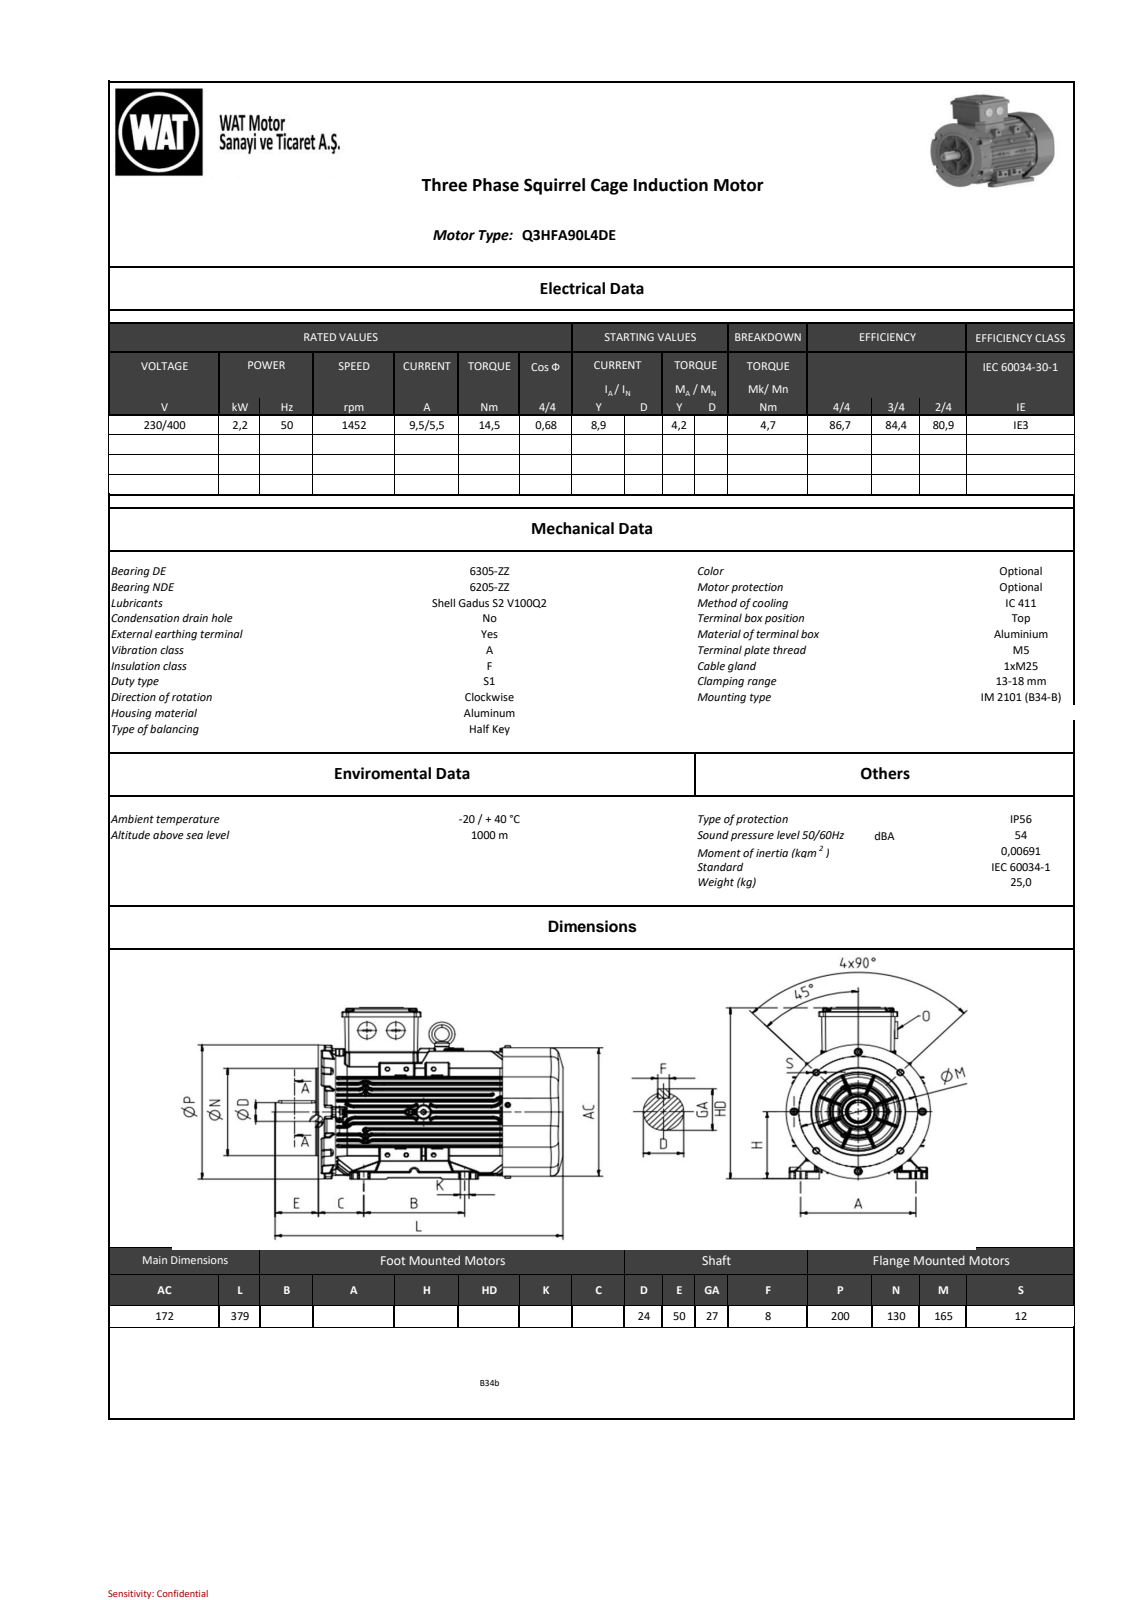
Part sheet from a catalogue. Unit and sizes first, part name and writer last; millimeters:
Units: millimetres
Overall size (bounding box): 378.54 × 233.05 × 200
Round holes (diameter × count): ⌀11 ×4, ⌀12 ×4, ⌀3.5 ×1, ⌀5 ×1, ⌀6.8 ×1, ⌀8.4 ×1, ⌀9.87 ×1, ⌀37.42 ×1, ⌀79.79 ×1, ⌀97.79 ×1, ⌀115.78 ×1
Round bosses / shafts (diameter × count): ⌀8 ×6, ⌀25 ×3, ⌀200 ×1, ⌀130 ×1, ⌀102.19 ×1, ⌀84.19 ×1, ⌀27.5 ×1, ⌀24 ×1
Partial cylindrical surfaces — rounded edges, fillets, slot ends (radius × count): R0.8 ×571, R1 ×456, R0.5 ×182, R2 ×50, R8 ×28, R4 ×10, R5.68 ×7, R0.25 ×6
Main face-to-face distances: 7.5, 91.91, 8.93, 82.98, 23.57, 50.35, 1.25, 7.37, 90.35, 16.87
Hole centre spacings: 62, 149.54, 79.39, 82.46, 112.27, 116.62, 82.43, 82.5
Bodies: 0 solids, 5822 faces (1467 planar, 2077 cylindrical, 2278 other)
Part name (STEP PRODUCT): model1
STEP written by: SIEMENS PLM Software NX2206.8101 (AUTOMOTIVE_DESIGN)
